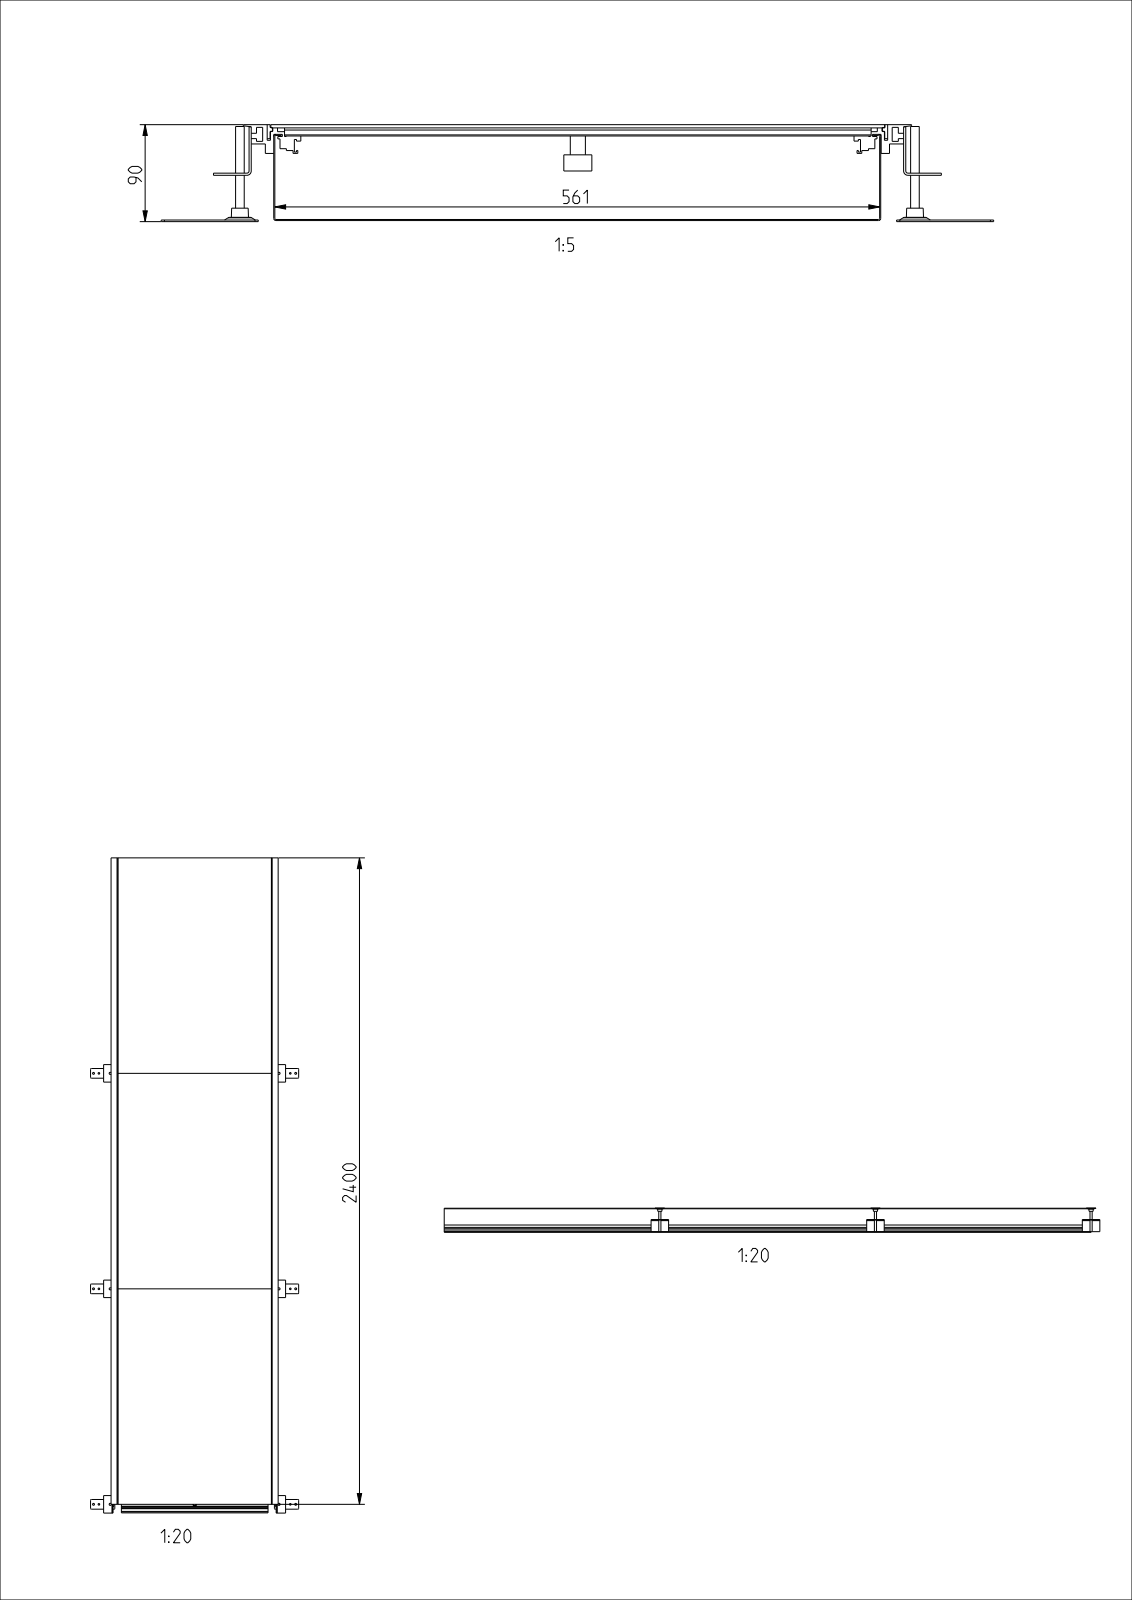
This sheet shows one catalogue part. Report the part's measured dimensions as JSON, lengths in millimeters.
{"part_name": "U05644KUN; U05650KUN; U05647KUN; U05826KUN (+8 more)", "step_written_by": "CREO PARAMETRIC BY PTC INC, 2020281 (AUTOMOTIVE_DESIGN)", "units": "millimeters", "bodies": {"solids": 61, "faces": 1036, "planar": 606, "cylindrical": 358, "other": 72}, "overall_size": [2432.5, 772.13, 90], "volume_mm3": 10410000, "surface_area_mm2": 8783000, "round_holes": [[7, 15], [8, 9], [10, 9], [6, 6], [8.5, 6], [11.5, 6], [17.5, 6], [23, 6]], "round_bosses_or_shafts": [[26, 9], [14, 9], [11.9, 9], [20, 6], [8, 6]], "partial_cylinders_radius": [[2, 96], [3, 24], [0.5, 20], [1, 4], [4, 2]], "face_to_face_distances": [1, 3, 86, 89, 85, 88, 562, 7.5, 6.5, 78.5], "hole_center_spacings": [800, 1600, 800.25, 801.1, 802.4, 1042.3, 1055.24, 1083.09]}
